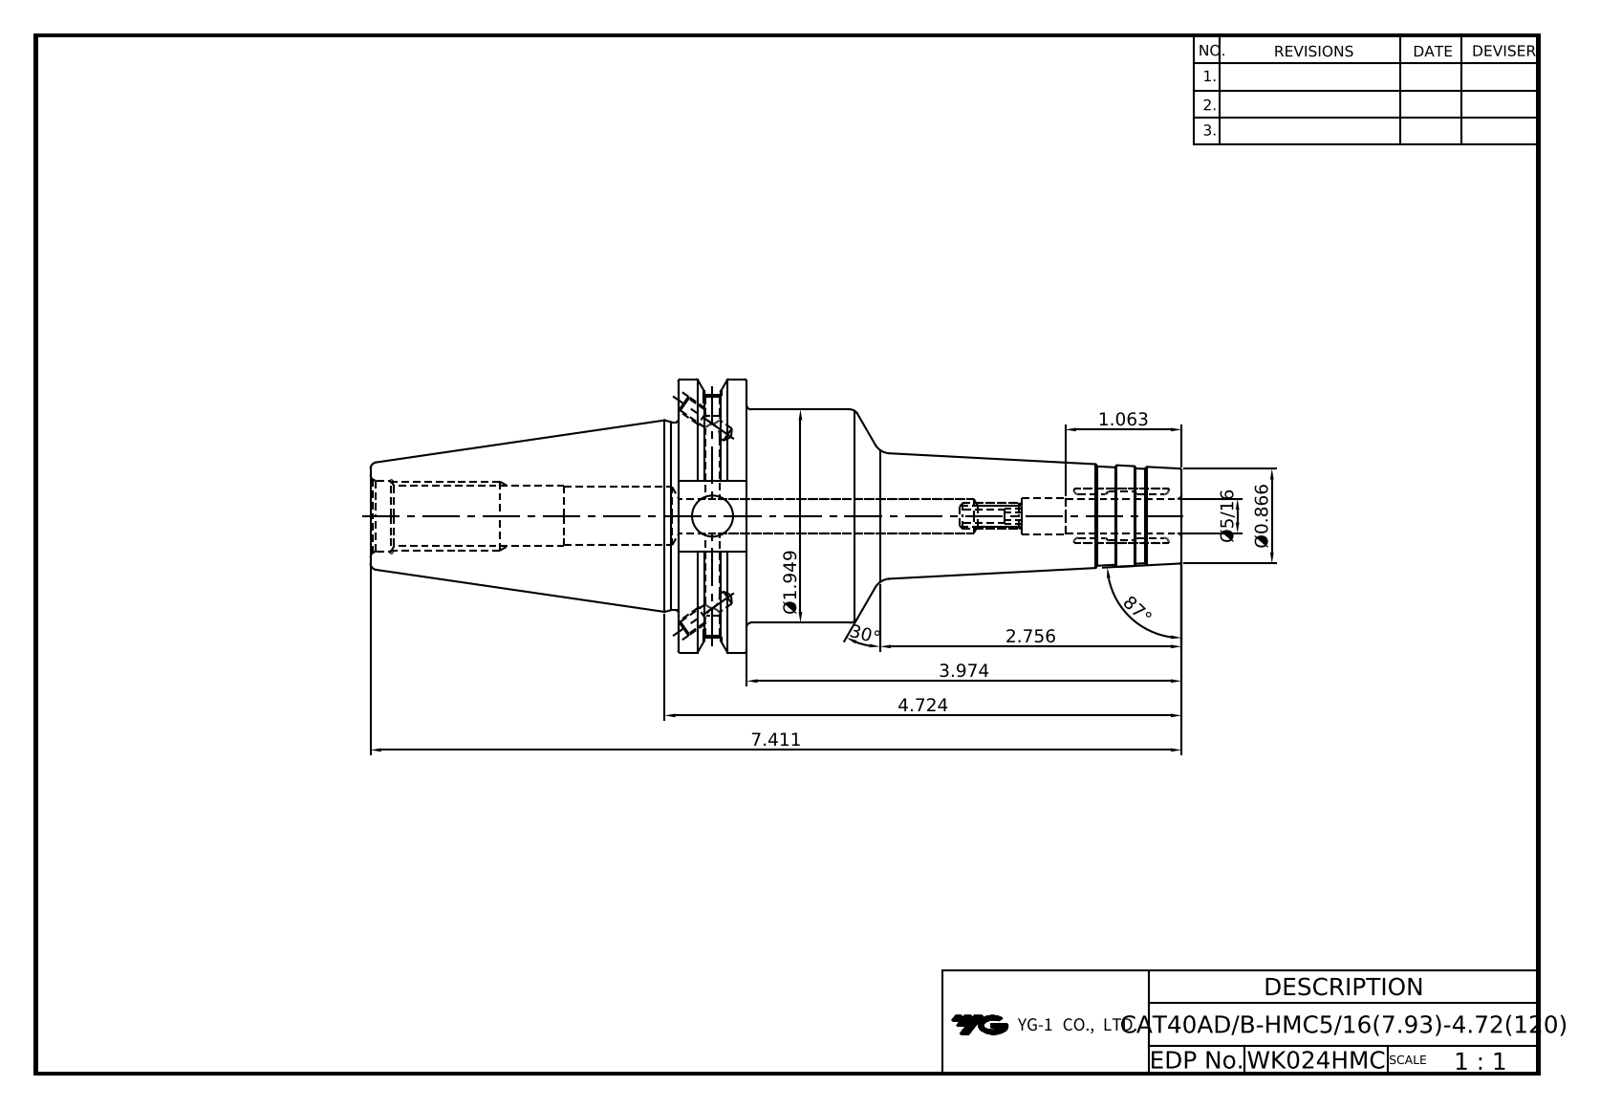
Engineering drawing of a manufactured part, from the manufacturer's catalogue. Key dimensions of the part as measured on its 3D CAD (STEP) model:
Part name (STEP PRODUCT): LO-CAT40ADB-HMC7.9375-4.72
STEP written by: Autodesk Inventor 2020 (AUTOMOTIVE_DESIGN)
Units: millimetres
Bodies: 1 solid, 108 faces (36 planar, 31 cylindrical, 41 other)
Overall size (bounding box): 188.25 × 63.5 × 61.09
Volume: 188 995 mm³ · Surface area: 32 537 mm²
Round holes (diameter × count): ⌀3.24 ×4, ⌀4 ×2, ⌀4.2 ×2, ⌀4.92 ×1, ⌀7.94 ×1, ⌀8 ×1, ⌀9.5 ×1, ⌀9.53 ×1, ⌀13 ×1, ⌀13.39 ×1, ⌀16.3 ×1
Round bosses / shafts (diameter × count): ⌀63.5 ×1, ⌀49.5 ×1, ⌀43.6 ×1
Partial cylindrical surfaces — rounded edges, fillets, slot ends (radius × count): R8.19 ×1, R28.15 ×1
Main face-to-face distances: 15.88, 116.83, 100.95, 47.6, 16.38, 71.42, 87.3, 188.25, 77.47, 6.05
